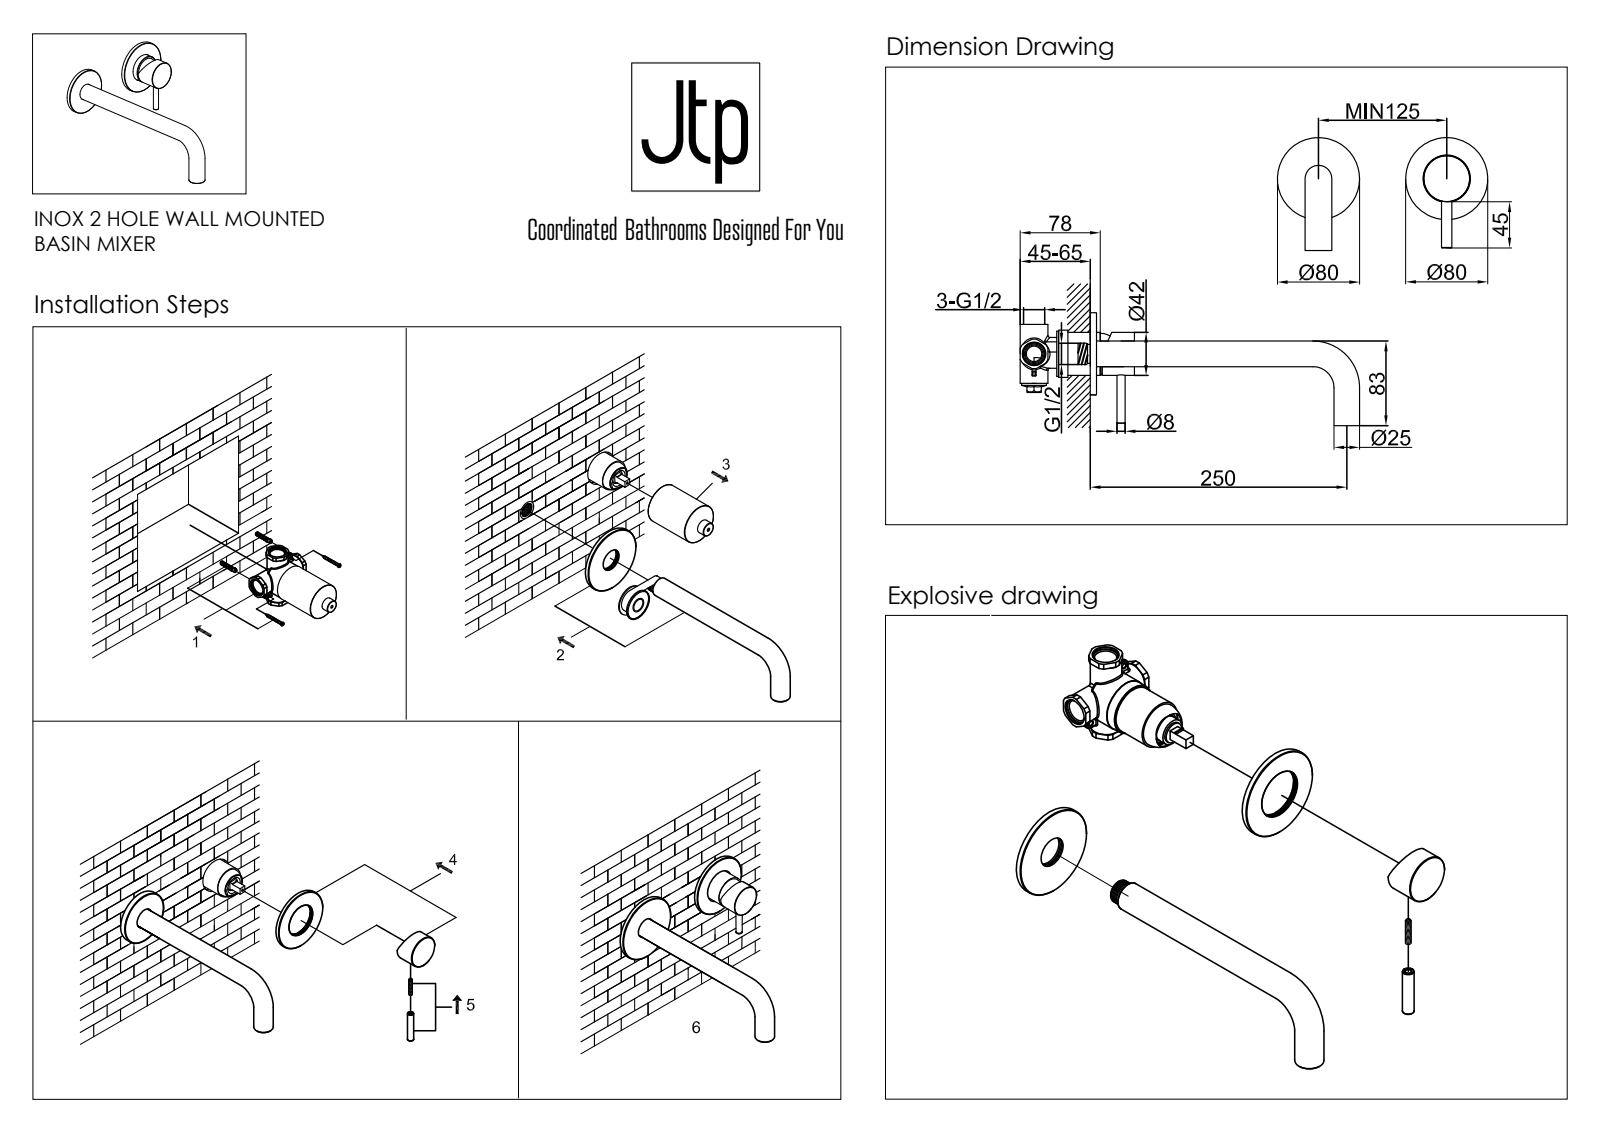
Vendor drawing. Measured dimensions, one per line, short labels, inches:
name: 092
written by: PRO/ENGINEER BY PARAMETRIC TECHNOLOGY CORPORATION, 2012130 (CONFIG_CONTROL_DESIGN)
unit: in
bodies: 5 solids, 35 faces (11 planar, 18 cylindrical, 6 other)
size: 262.5 × 205 × 123
volume: 292 237 in³; area: 60 993 in²
holes: 1× ⌀25.5, 1× ⌀42.5
bosses: 2× ⌀80, 2× ⌀25, 1× ⌀42, 1× ⌀8
face distances: 8, 20, 51.5, 12, 43.5, 31.5, 18, 10, 2, 33.5
hole spacings: 125
